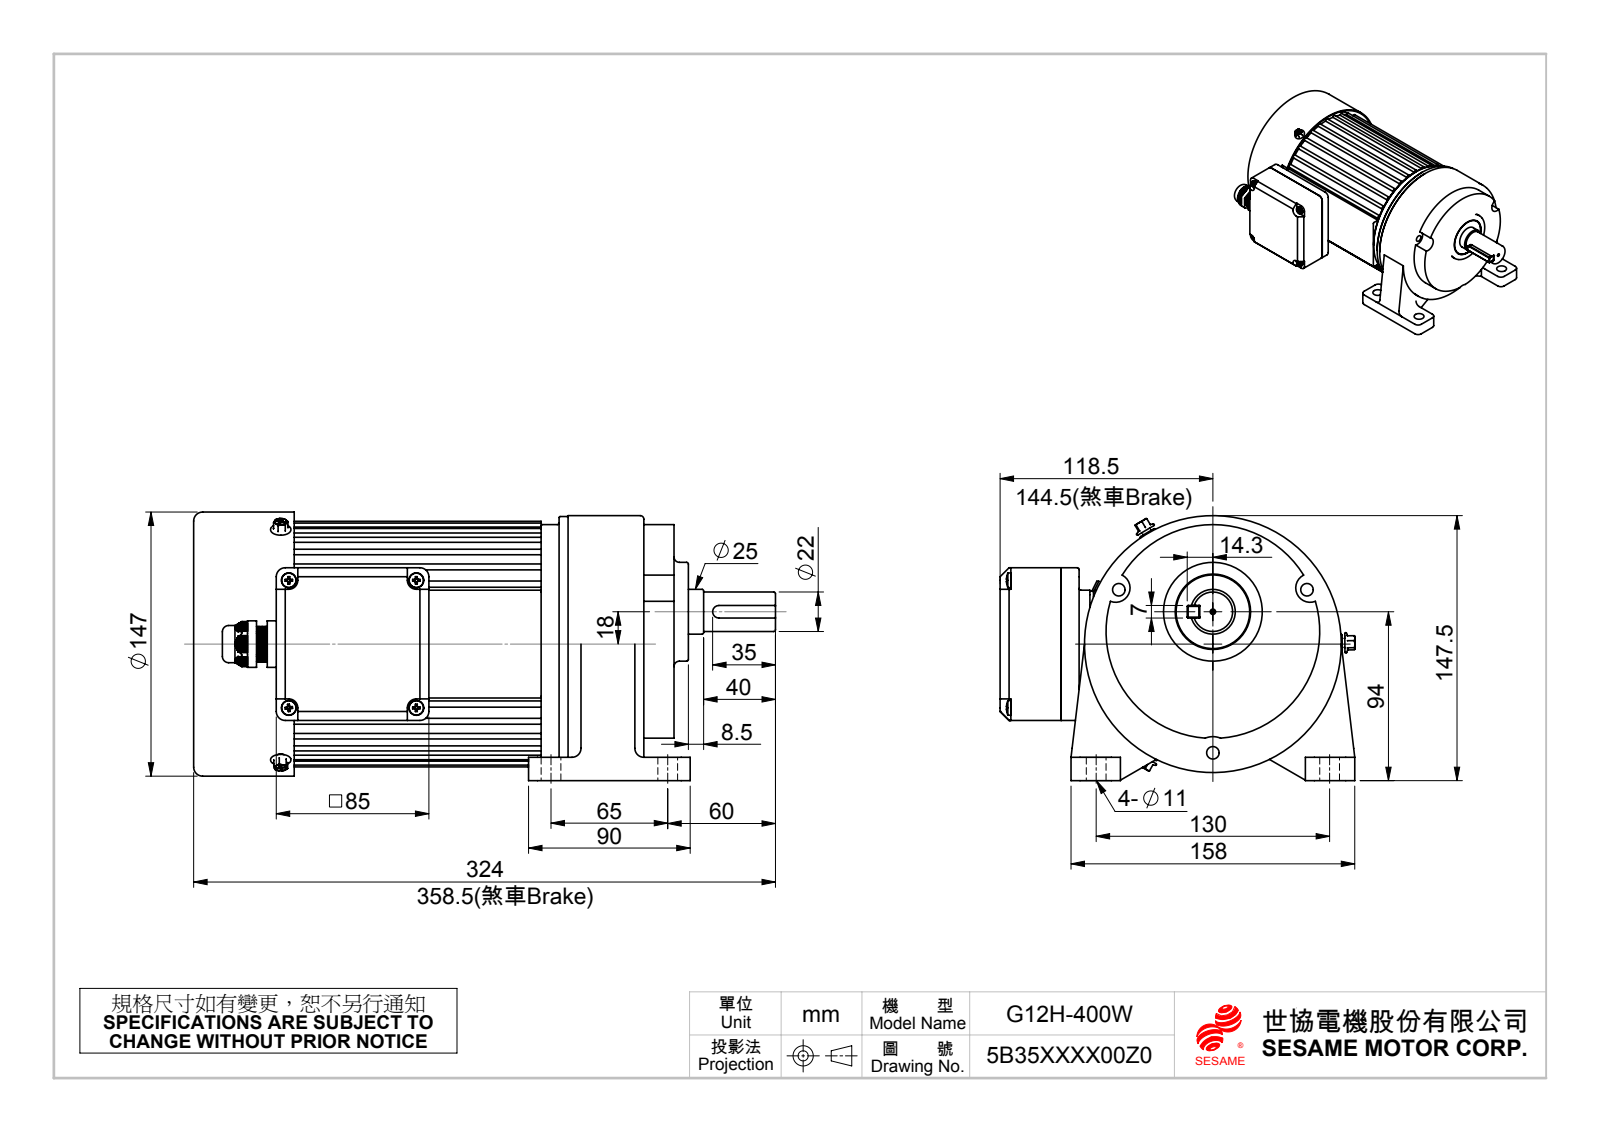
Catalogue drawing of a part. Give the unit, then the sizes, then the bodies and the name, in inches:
Units: inches
Overall size (bounding box): 12.756 × 7.781 × 5.886
Round holes (diameter × count): ⌀0.197 ×14, ⌀0.13 ×9, ⌀0.236 ×5, ⌀0.315 ×4, ⌀0.433 ×4, ⌀0.276 ×3, ⌀0.079 ×1, ⌀0.425 ×1, ⌀0.65 ×1, ⌀0.982 ×1, ⌀1.654 ×1, ⌀5.709 ×1
Round bosses / shafts (diameter × count): ⌀0.327 ×4, ⌀0.157 ×4, ⌀0.197 ×3, ⌀5.787 ×1, ⌀5.63 ×1, ⌀5.591 ×1, ⌀5.236 ×1, ⌀5.197 ×1
Partial cylindrical surfaces — rounded edges, fillets, slot ends (radius × count): R0.073 ×31, R0.039 ×26, R0.02 ×24, R0.197 ×18, R0.108 ×6, R0.079 ×4, R0.1 ×4, R0.14 ×4
Main face-to-face distances: 6.299, 1.732, 5.512, 0.787, 2.579, 0.374, 5.886, 6.673, 0.217, 0.472
Hole centre spacings: 1.772, 2.507, 2.795, 2.382, 0.433, 0.453, 0.575, 0.582
Volume: 241.4 in³ · Surface area: 642 in²
Bodies: 19 solids, 2606 faces (812 planar, 781 cylindrical, 1013 other)
Part name (STEP PRODUCT): G12OS1-02; 7x7xL_35L; 出線盒上蓋; 出線盒墊片JTH-UP3(PVC2mm厚) (+8 more)
STEP written by: SolidWorks 2010 (CONFIG_CONTROL_DESIGN)
